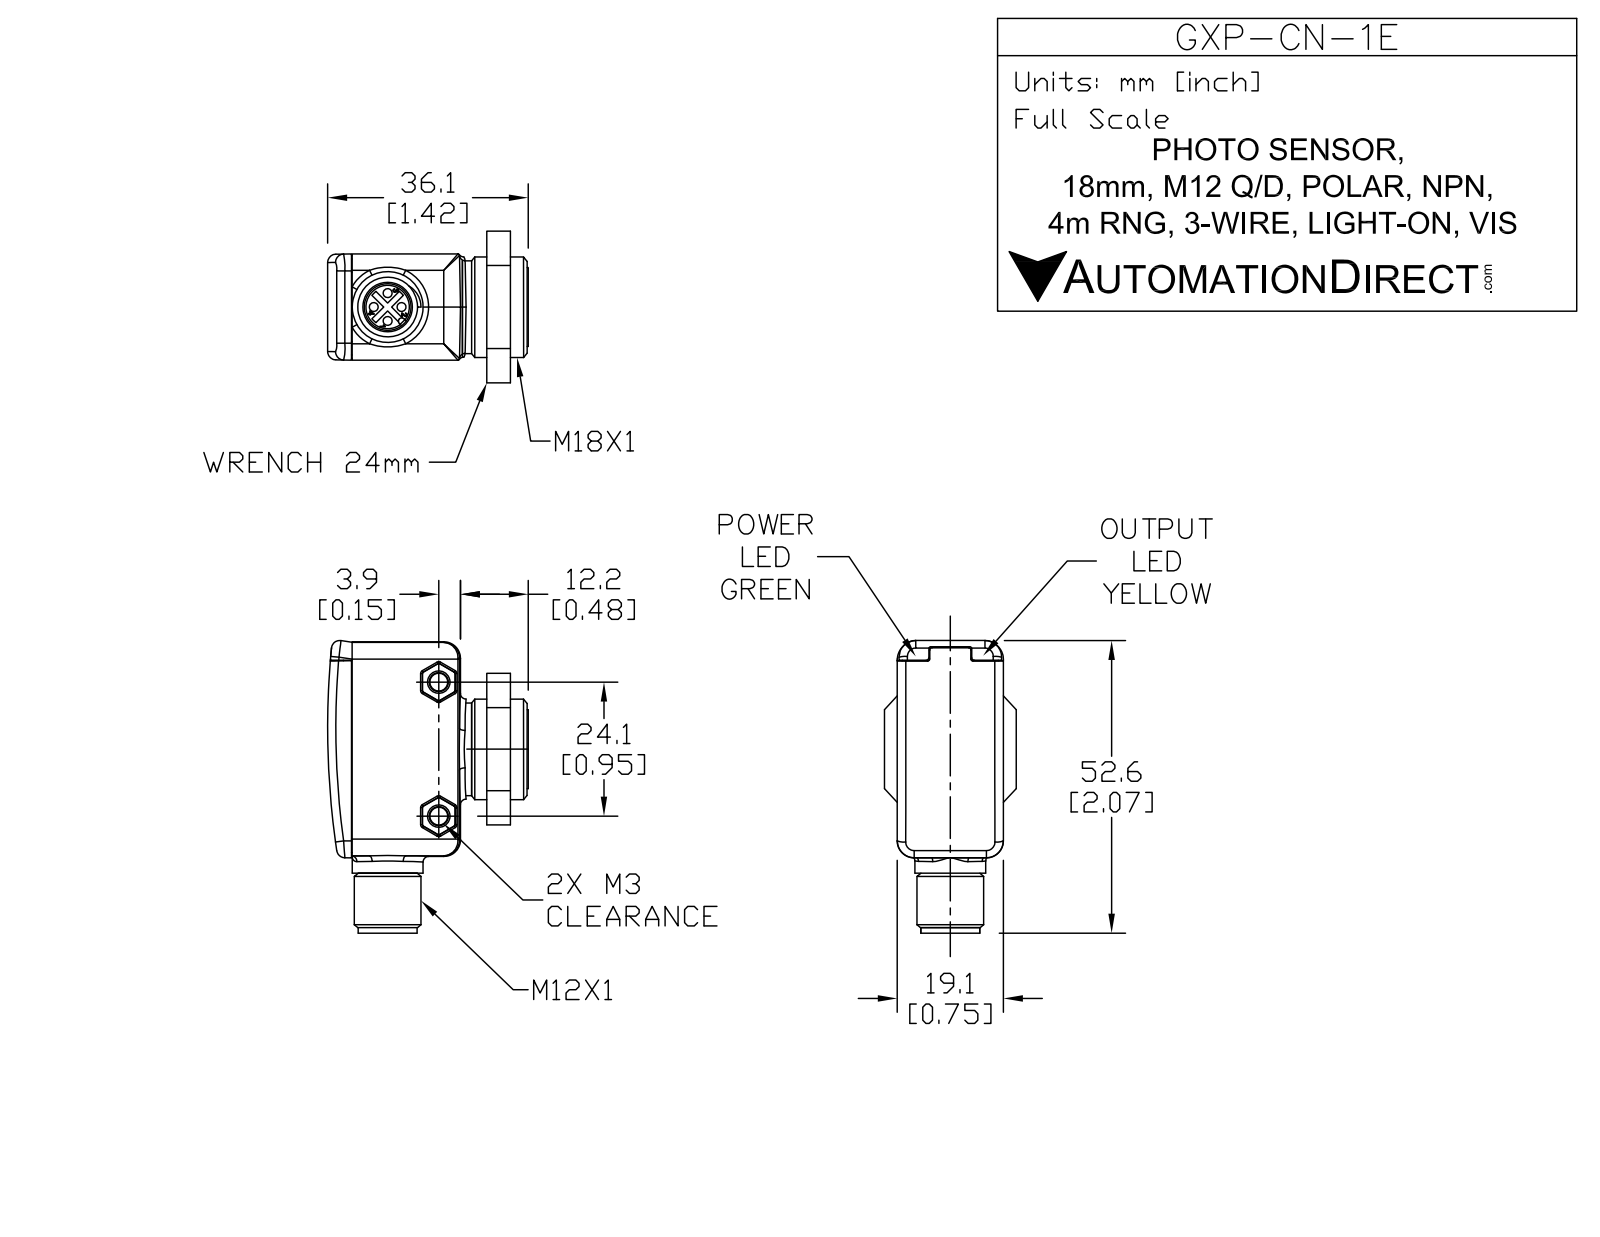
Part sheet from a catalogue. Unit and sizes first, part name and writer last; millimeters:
Units: millimetres
Overall size (bounding box): 52.66 × 36.1 × 23.85
Round holes (diameter × count): ⌀3.2 ×2, ⌀8.36 ×1
Round bosses / shafts (diameter × count): ⌀18 ×1, ⌀17.5 ×1, ⌀14.2 ×1, ⌀12.68 ×1, ⌀11.55 ×1, ⌀10.6 ×1
Partial cylindrical surfaces — rounded edges, fillets, slot ends (radius × count): R1.5 ×8, R1 ×4, R139.57 ×1
Main face-to-face distances: 19.1, 7.2, 2.12, 9.32, 19.2, 5, 2.88, 12.2, 38.8, 5.95
Hole centre spacings: 24.1
Volume: 21 253 mm³ · Surface area: 6 452 mm²
Bodies: 1 solid, 107 faces (60 planar, 33 cylindrical, 14 other)
Part name (STEP PRODUCT): GXP-CN-1E
STEP written by: SolidWorks 2013 (AUTOMOTIVE_DESIGN)
